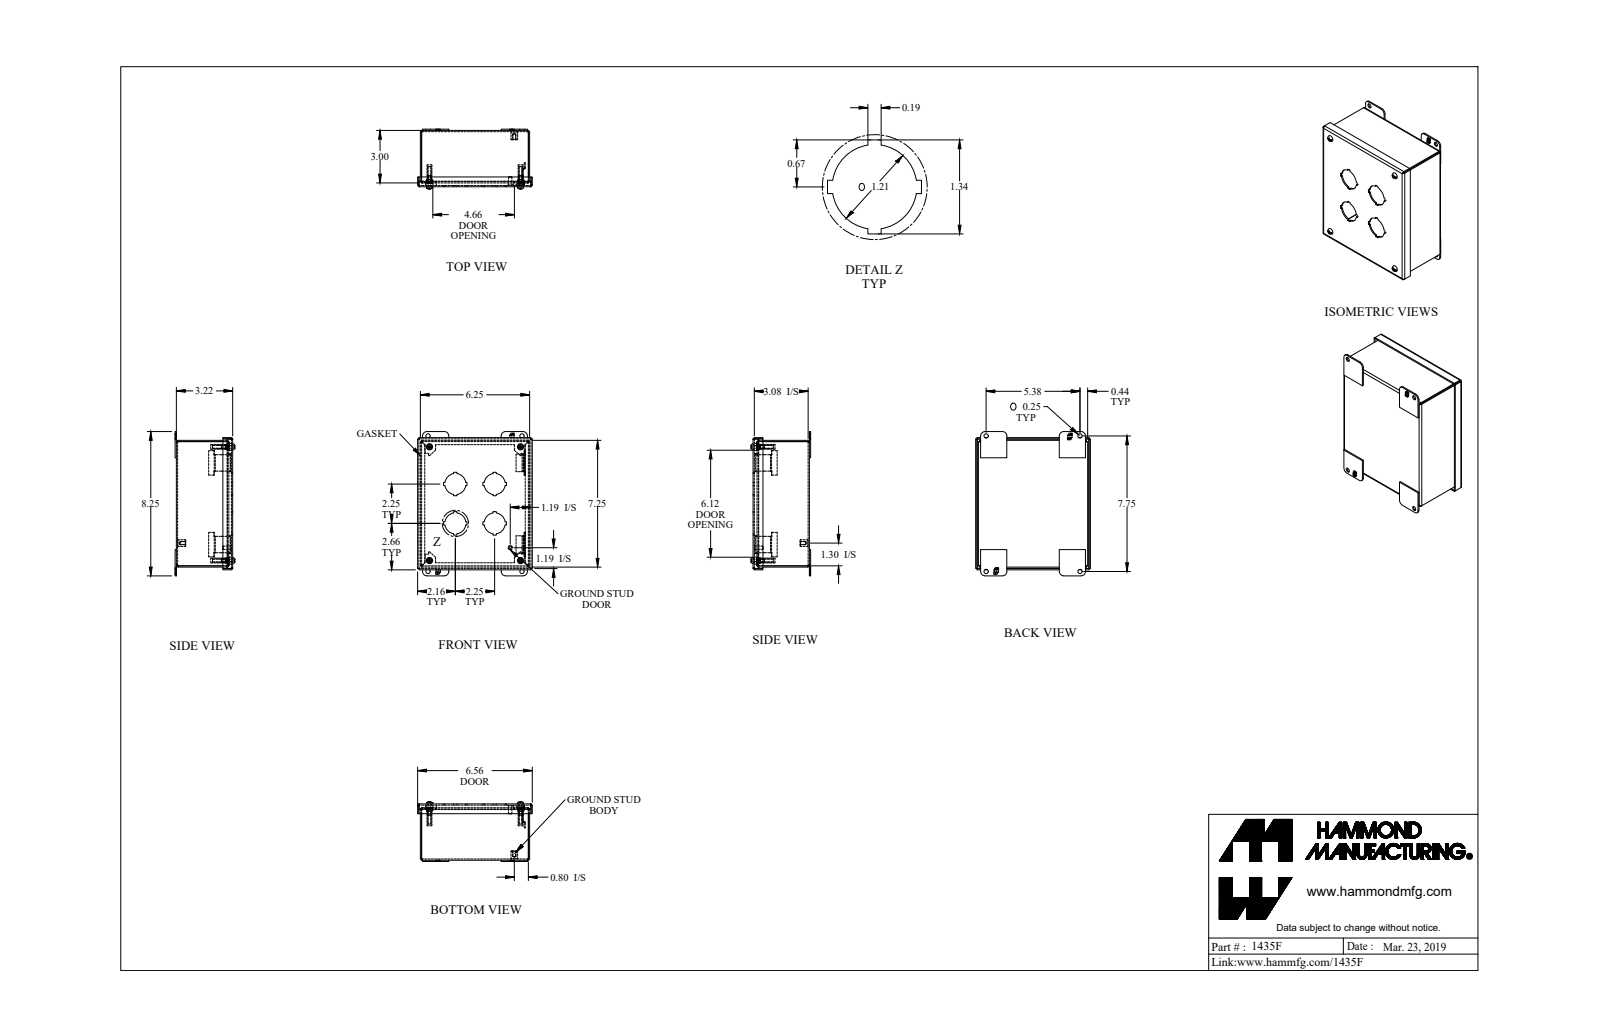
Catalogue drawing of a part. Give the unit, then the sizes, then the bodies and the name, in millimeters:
Units: millimetres
Overall size (bounding box): 209.6 × 166.7 × 86.9
Round holes (diameter × count): ⌀6.4 ×8, ⌀4 ×4, ⌀10.3 ×4, ⌀30.7 ×4, ⌀4 ×1
Round bosses / shafts (diameter × count): ⌀9.9 ×4, ⌀7 ×4, ⌀4.8 ×4, ⌀3.8 ×4, ⌀9.5 ×1, ⌀6.4 ×1, ⌀4.8 ×1
Partial cylindrical surfaces — rounded edges, fillets, slot ends (radius × count): R0.6 ×12, R2 ×12, R6.4 ×8, R0.7 ×4, R0.9 ×4, R2.2 ×4, R2.7 ×4, R4.1 ×4
Main face-to-face distances: 1.4, 1.8, 80, 81.8, 78.6, 80.4, 157.3, 1.4, 182.7, 158.8
Hole centre spacings: 165.1, 181, 117.3, 16, 57.2, 65.8, 132.3, 132.4
Volume: 249 700 mm³ · Surface area: 291 600 mm²
Bodies: 23 solids, 785 faces (545 planar, 184 cylindrical, 56 other)
Part name (STEP PRODUCT): 1435F_Default
STEP written by: SolidWorks 2019 (CONFIG_CONTROL_DESIGN)
